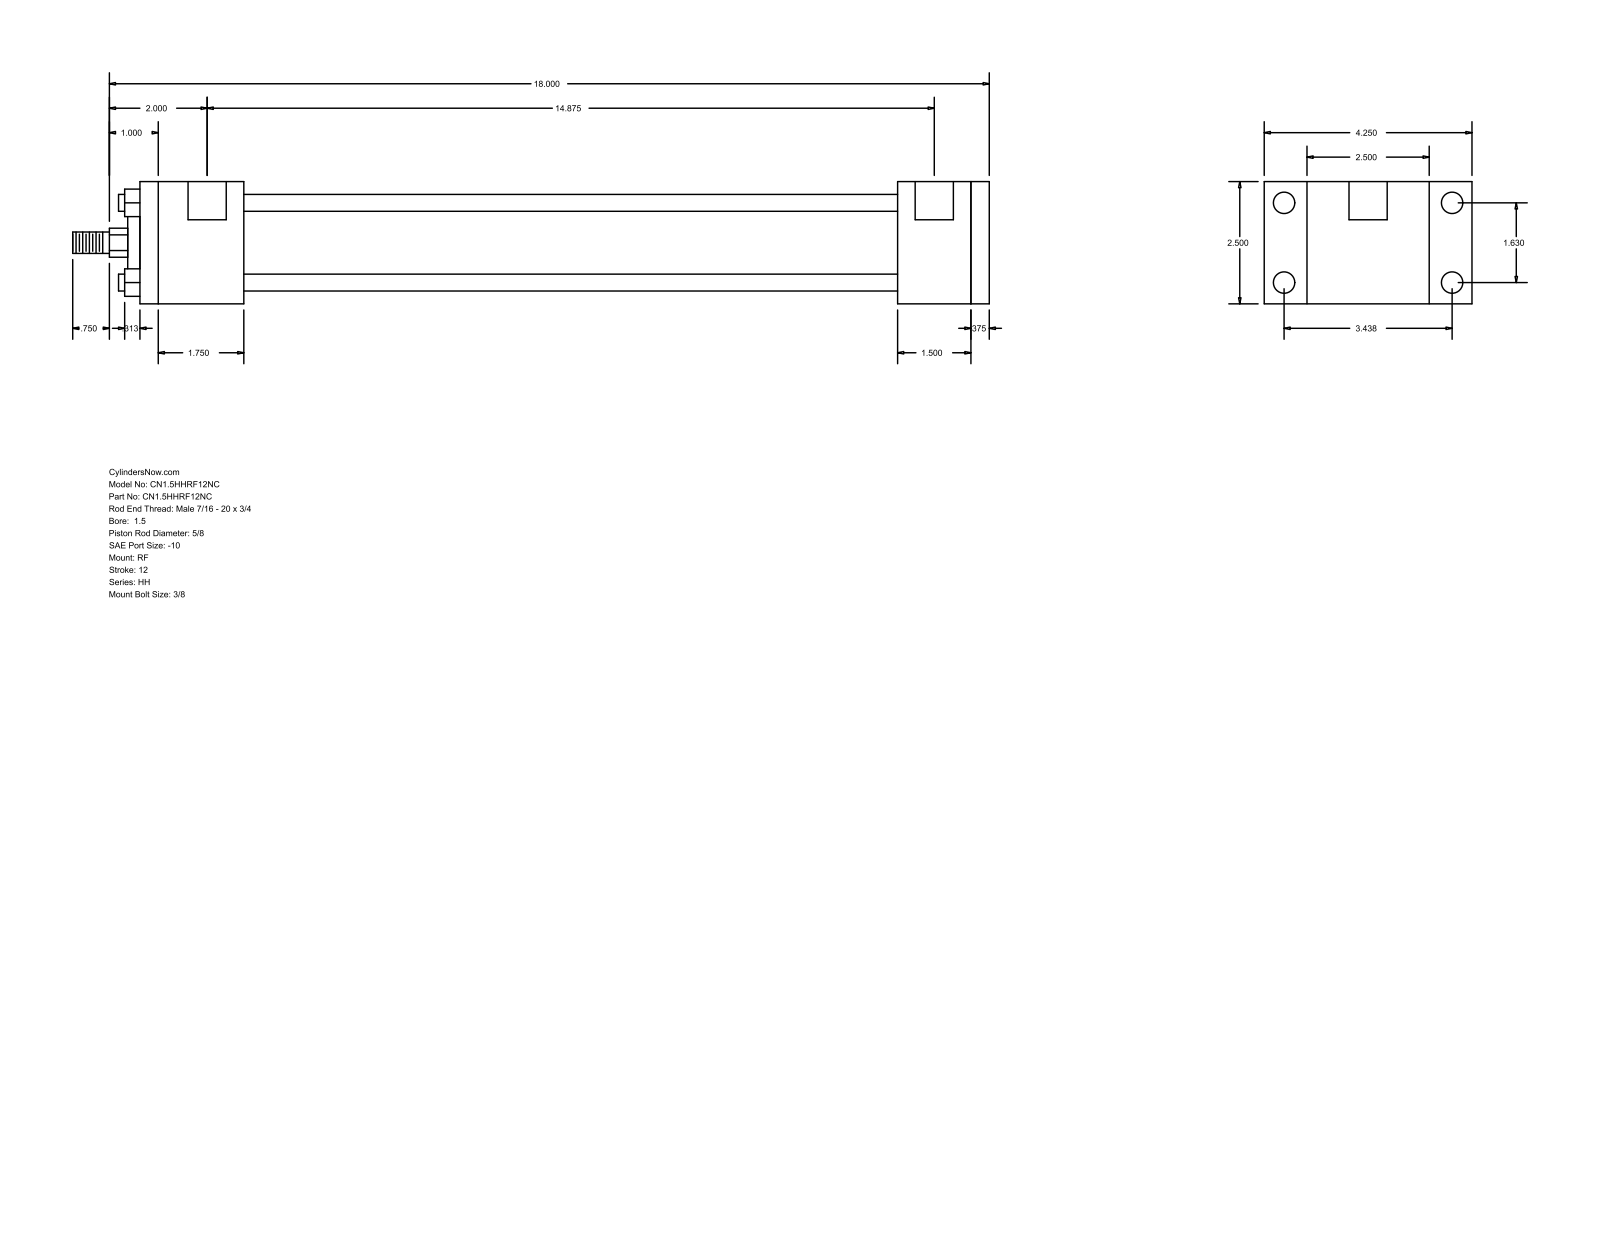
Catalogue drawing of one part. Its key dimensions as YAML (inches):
part_name: "HH_RF__0150_0.625"
step_written_by: "GSSL Pune (CONFIG_CONTROL_DESIGN)"
units: inches
bodies: {solids: 0, faces: 92, planar: 64, cylindrical: 28, other: 0}
overall_size: [18.75, 4.25, 2.5]
round_holes:
  - {diameter: 0.219, count: 4}
  - {diameter: 0.438, count: 4}
  - {diameter: 0.781, count: 2}
round_bosses_or_shafts:
  - {diameter: 0.345, count: 4}
  - {diameter: 1.75, count: 1}
  - {diameter: 1.125, count: 1}
  - {diameter: 0.625, count: 1}
  - {diameter: 0.437, count: 1}
partial_cylinders:
  - {radius: 0.297, count: 1}
face_to_face_distances: [2.5, 17.375, 17, 0.375, 1.875, 2.125, 15.5, 13.375, 14.875, 15.25]
hole_center_spacings: [0.063, 1.63, 3.438, 3.805, 14.937, 15, 14.875]
